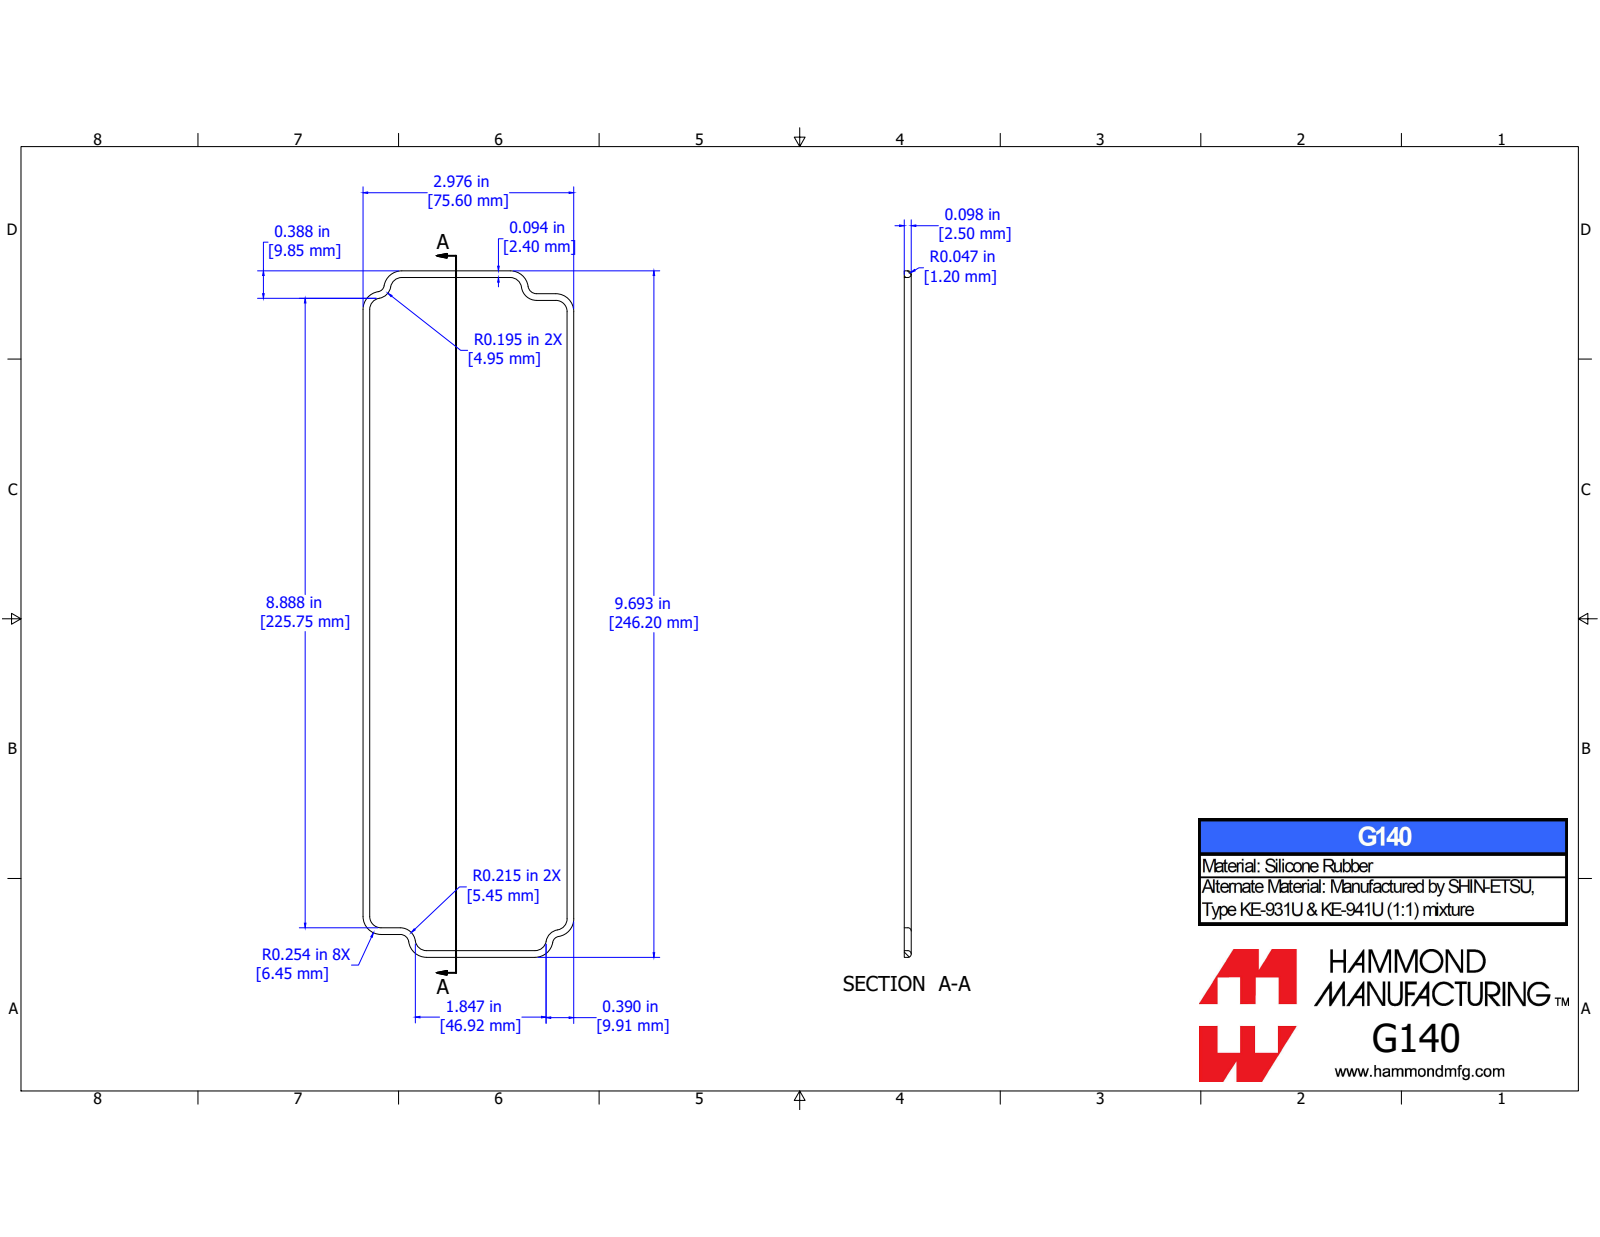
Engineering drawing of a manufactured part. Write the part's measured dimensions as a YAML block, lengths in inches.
part_name: "1590Z140G"
step_written_by: "SolidWorks 2019 (CONFIG_CONTROL_DESIGN)"
units: inches
bodies: {solids: 1, faces: 55, planar: 13, cylindrical: 30, other: 12}
overall_size: [9.72, 3.047, 0.118]
volume: 0.248
surface_area: 9.352
partial_cylinders:
  - {radius: 0.11, count: 8}
  - {radius: 0.205, count: 8}
  - {radius: 0.047, count: 6}
  - {radius: 0.12, count: 2}
  - {radius: 0.15, count: 2}
  - {radius: 0.215, count: 2}
  - {radius: 0.244, count: 2}
face_to_face_distances: [0.094, 2.953, 3.047, 2.858, 9.626, 9.531, 9.72, 9.291, 0.335, 0.429]
